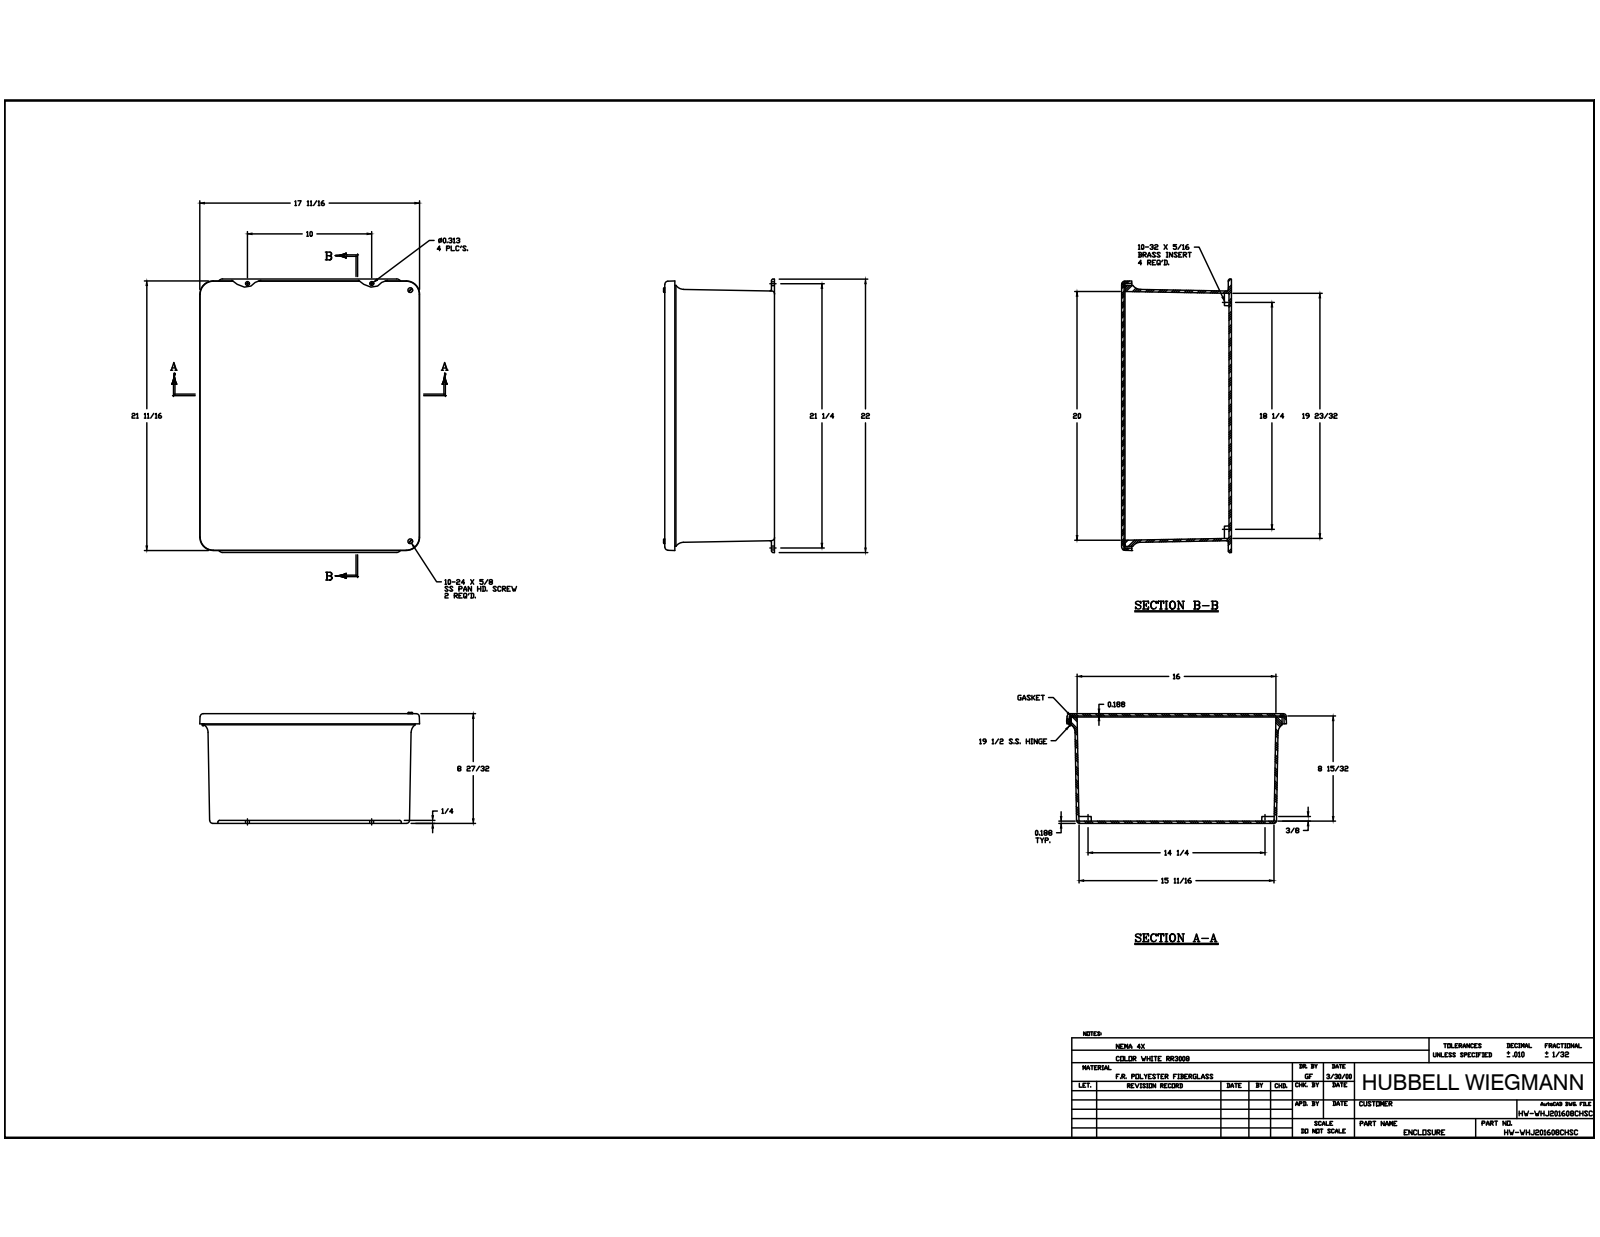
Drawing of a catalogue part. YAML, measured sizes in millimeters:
part_name: "J2016HW_1; RMINS45821P_9; RMINS45821P_10; RMINS45821P_11 (+8 more)"
step_written_by: "Autodesk Inventor 2014 (AUTOMOTIVE_DESIGN)"
units: millimeters
bodies: {solids: 26, faces: 977, planar: 393, cylindrical: 383, other: 201}
overall_size: [558.8, 449.85, 227.59]
volume: 4636000
surface_area: 1896000
round_holes:
  - {diameter: 3.33, count: 12}
  - {diameter: 3.56, count: 12}
  - {diameter: 3.86, count: 5}
  - {diameter: 3.96, count: 4}
  - {diameter: 5.54, count: 4}
  - {diameter: 3.68, count: 2}
  - {diameter: 2.16, count: 1}
round_bosses_or_shafts:
  - {diameter: 6.35, count: 12}
  - {diameter: 3.17, count: 12}
  - {diameter: 6.86, count: 6}
  - {diameter: 4.83, count: 2}
  - {diameter: 3.97, count: 2}
  - {diameter: 3.94, count: 1}
partial_cylinders:
  - {radius: 0.79, count: 20}
  - {radius: 3.17, count: 10}
  - {radius: 6.35, count: 8}
  - {radius: 5.08, count: 5}
  - {radius: 1.59, count: 4}
  - {radius: 9.53, count: 4}
  - {radius: 19.05, count: 4}
face_to_face_distances: [4.76, 219.5, 224.26, 4.77, 214.73, 219.49, 7.94, 12.7, 217.49, 212.72]
hole_center_spacings: [95.25, 190.5, 6.35, 88.9, 101.6, 184.15, 196.85, 279.4]
